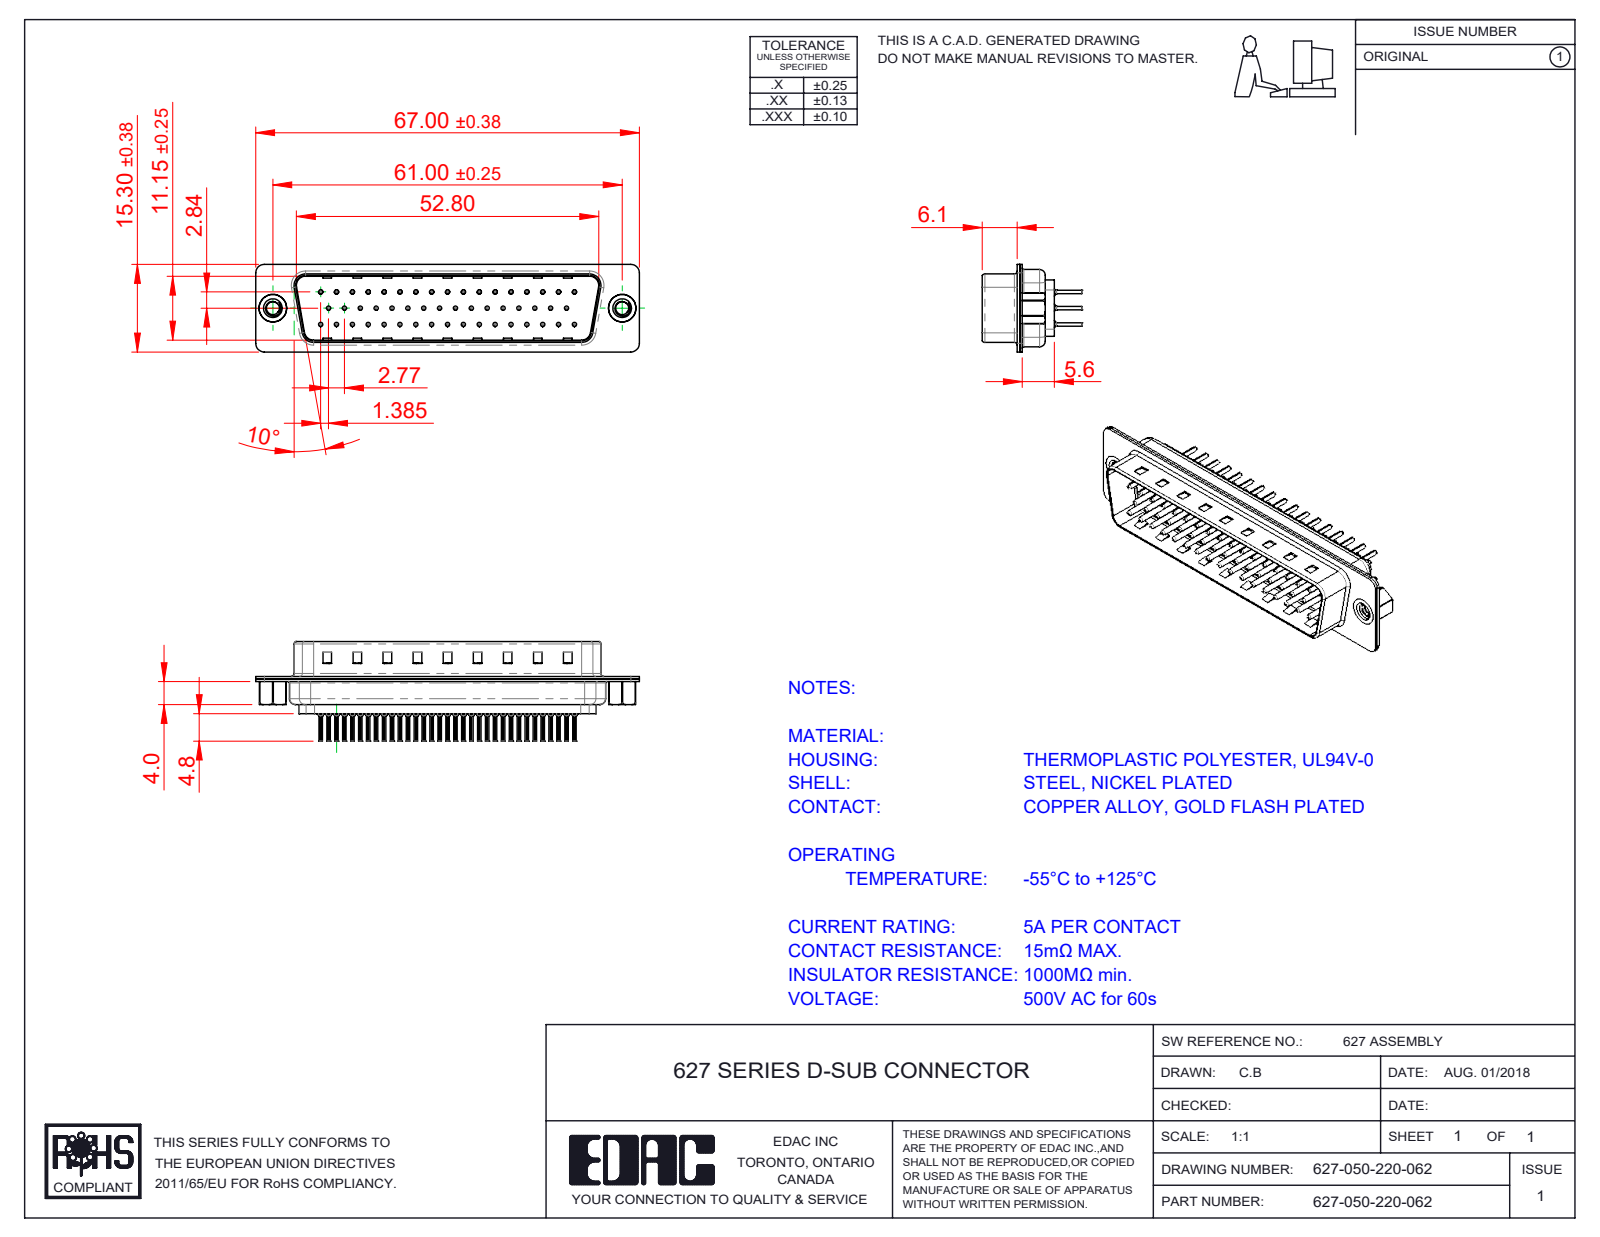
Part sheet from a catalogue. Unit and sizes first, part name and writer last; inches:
Units: inches
Overall size (bounding box): 2.638 × 0.681 × 0.602
Round holes (diameter × count): ⌀0.008 ×50, ⌀0.014 ×50, ⌀0.043 ×50, ⌀0.063 ×50, ⌀0.089 ×2, ⌀0.157 ×2, ⌀0.189 ×2
Round bosses / shafts (diameter × count): ⌀0.079 ×50, ⌀0.059 ×50, ⌀0.03 ×50, ⌀0.024 ×50, ⌀0.197 ×2, ⌀0.193 ×2
Partial cylindrical surfaces — rounded edges, fillets, slot ends (radius × count): R0.004 ×100, R0.059 ×16, R0.079 ×12, R0.02 ×8, R0.063 ×8, R0.01 ×4, R0.024 ×4, R0.026 ×4
Main face-to-face distances: 0.016, 0.018, 0.455, 0.035, 0.238, 0.256, 0.031, 0.485, 0.077, 0.03
Hole centre spacings: 0.124, 0.109, 0.218, 0.327, 0.436, 0.545, 0.654, 0.198
Volume: 0.27 in³ · Surface area: 19.49 in²
Bodies: 55 solids, 5308 faces (1403 planar, 1989 cylindrical, 1916 other)
Part name (STEP PRODUCT): 627 Housing_50 LP; 627 Contact Row 1_20L; 627 Contact Row 3_20L; 627 4-40 Threaded Rivet (+4 more)
STEP written by: SolidWorks 2020 (CONFIG_CONTROL_DESIGN)
